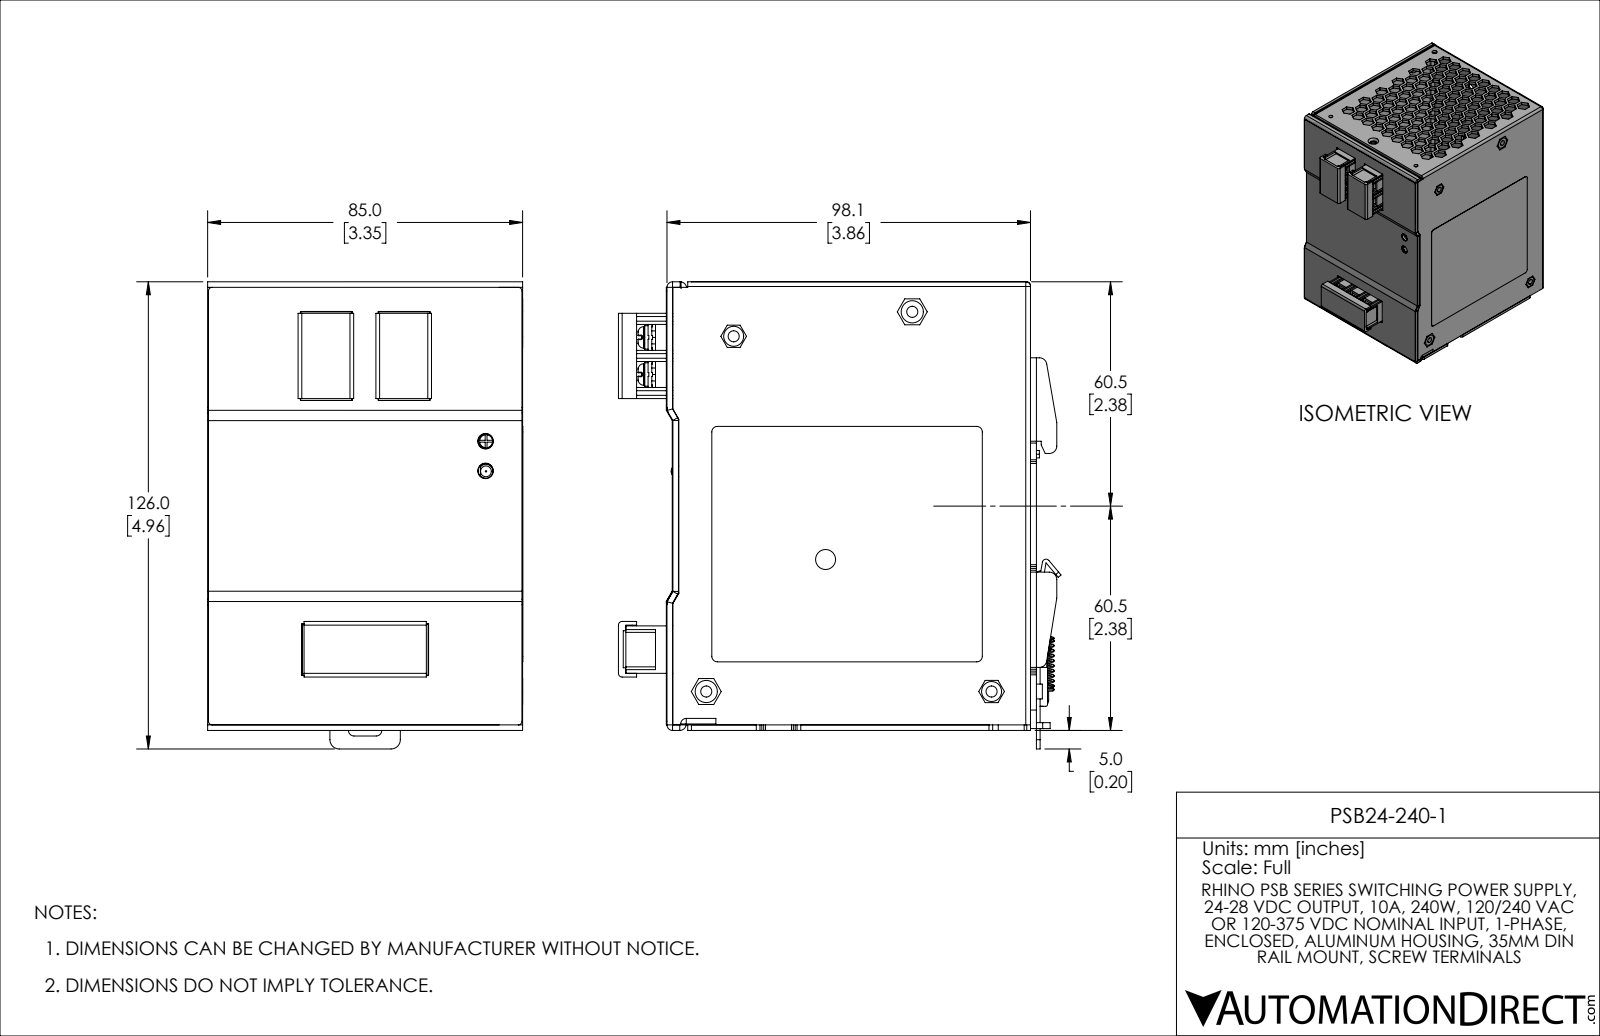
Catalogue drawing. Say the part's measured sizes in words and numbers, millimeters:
The part is named "PSB24-240-1". Its 3-D file was written by "SolidWorks 2021 (AUTOMOTIVE_DESIGN)". It is 35 solids with 3945 faces: 2994 planar, 611 cylindrical and 340 other. Overall it measures 126 by 119.5 by 85 millimeters. Its volume is 113 500 cubic millimeters and its surface area 188 600 square millimeters. Round holes: 8 of diameter 3, 5 of diameter 1, 4 of diameter 2.5, 4 of diameter 3.4, 2 of diameter 0.6, 2 of diameter 1.6, 2 of diameter 2, 2 of diameter 2.2, 2 of diameter 3.5, 2 of diameter 4, 2 of diameter 4.2, 1 of diameter 2.8. Round bosses or shafts: 8 of diameter 3.5, 7 of diameter 6.3, 7 of diameter 5.8, 6 of diameter 4, 3 of diameter 6, 3 of diameter 5.4, 1 of diameter 2.9. Partial cylindrical surfaces (rounded edges, fillets, slot ends): 98 of radius 0.5, 88 of radius 0.1, 56 of radius 1, 28 of radius 0.2, 15 of radius 1.5, 14 of radius 0.6, 12 of radius 2, 9 of radius 1.6. The main face-to-face distances are 1.5, 1.6, 83.5, 96.6, 6.2, 98.1, 91.9, 3.1, 95, 82. The hole center spacings are 10, 6.9, 8, 9.4, 12.2, 30.7, 32.5, 36.
